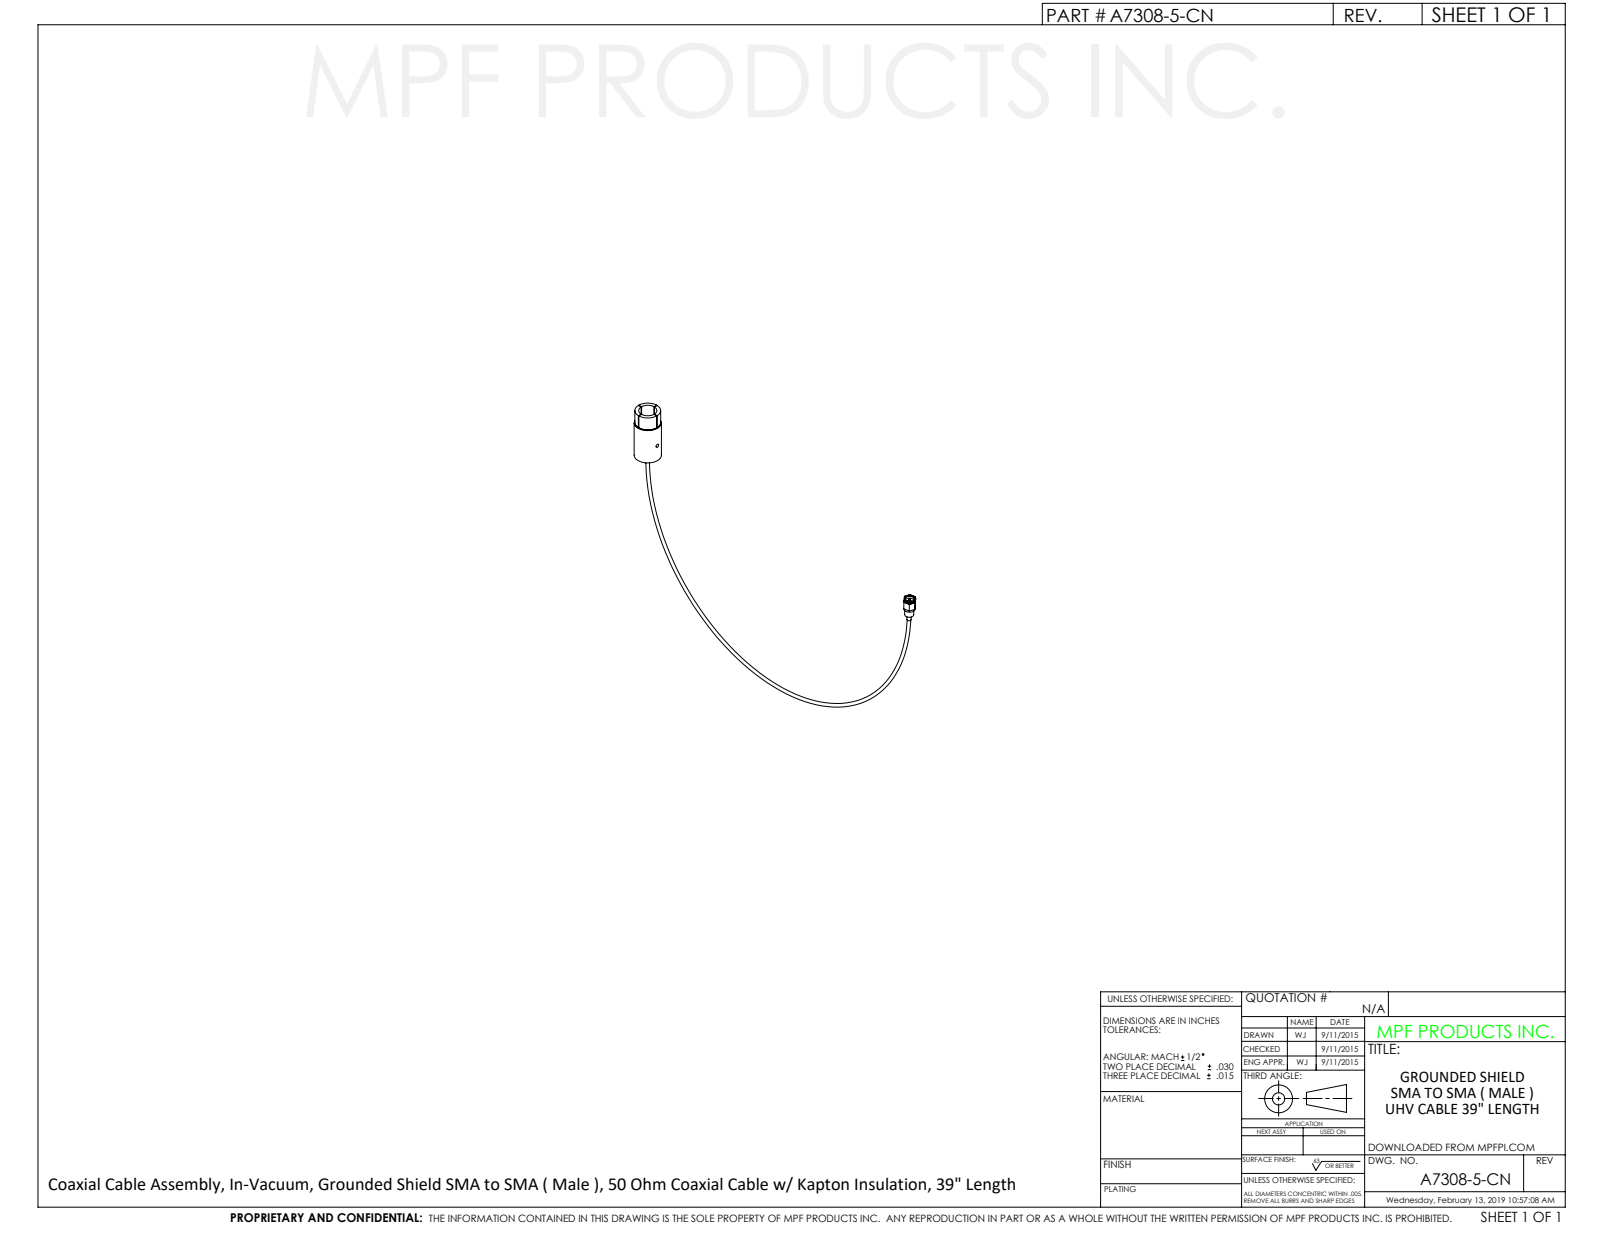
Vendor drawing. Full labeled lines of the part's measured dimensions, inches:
Part name (STEP PRODUCT): A7307-5-CN; A7300 MALE SMA PART; A7301-3_JUST CABLE
STEP written by: SolidWorks 2012 (CONFIG_CONTROL_DESIGN)
Units: inches
Bodies: 3 solids, 109 faces (52 planar, 50 cylindrical, 7 other)
Overall size (bounding box): 10.737 × 6.833 × 0.75
Volume: 0.535 in³ · Surface area: 13.37 in²
Round holes (diameter × count): ⌀0.1 ×2, ⌀0.05 ×1, ⌀0.115 ×1, ⌀0.167 ×1, ⌀0.186 ×1, ⌀0.257 ×1, ⌀0.293 ×1, ⌀0.5 ×1
Round bosses / shafts (diameter × count): ⌀0.75 ×1, ⌀0.71 ×1, ⌀0.307 ×1, ⌀0.294 ×1, ⌀0.25 ×1, ⌀0.207 ×1, ⌀0.18 ×1, ⌀0.165 ×1
Main face-to-face distances: 1.5, 0.2, 1.3, 0.02, 0.308, 0.308, 0.305, 0.214, 0.409, 0.104
